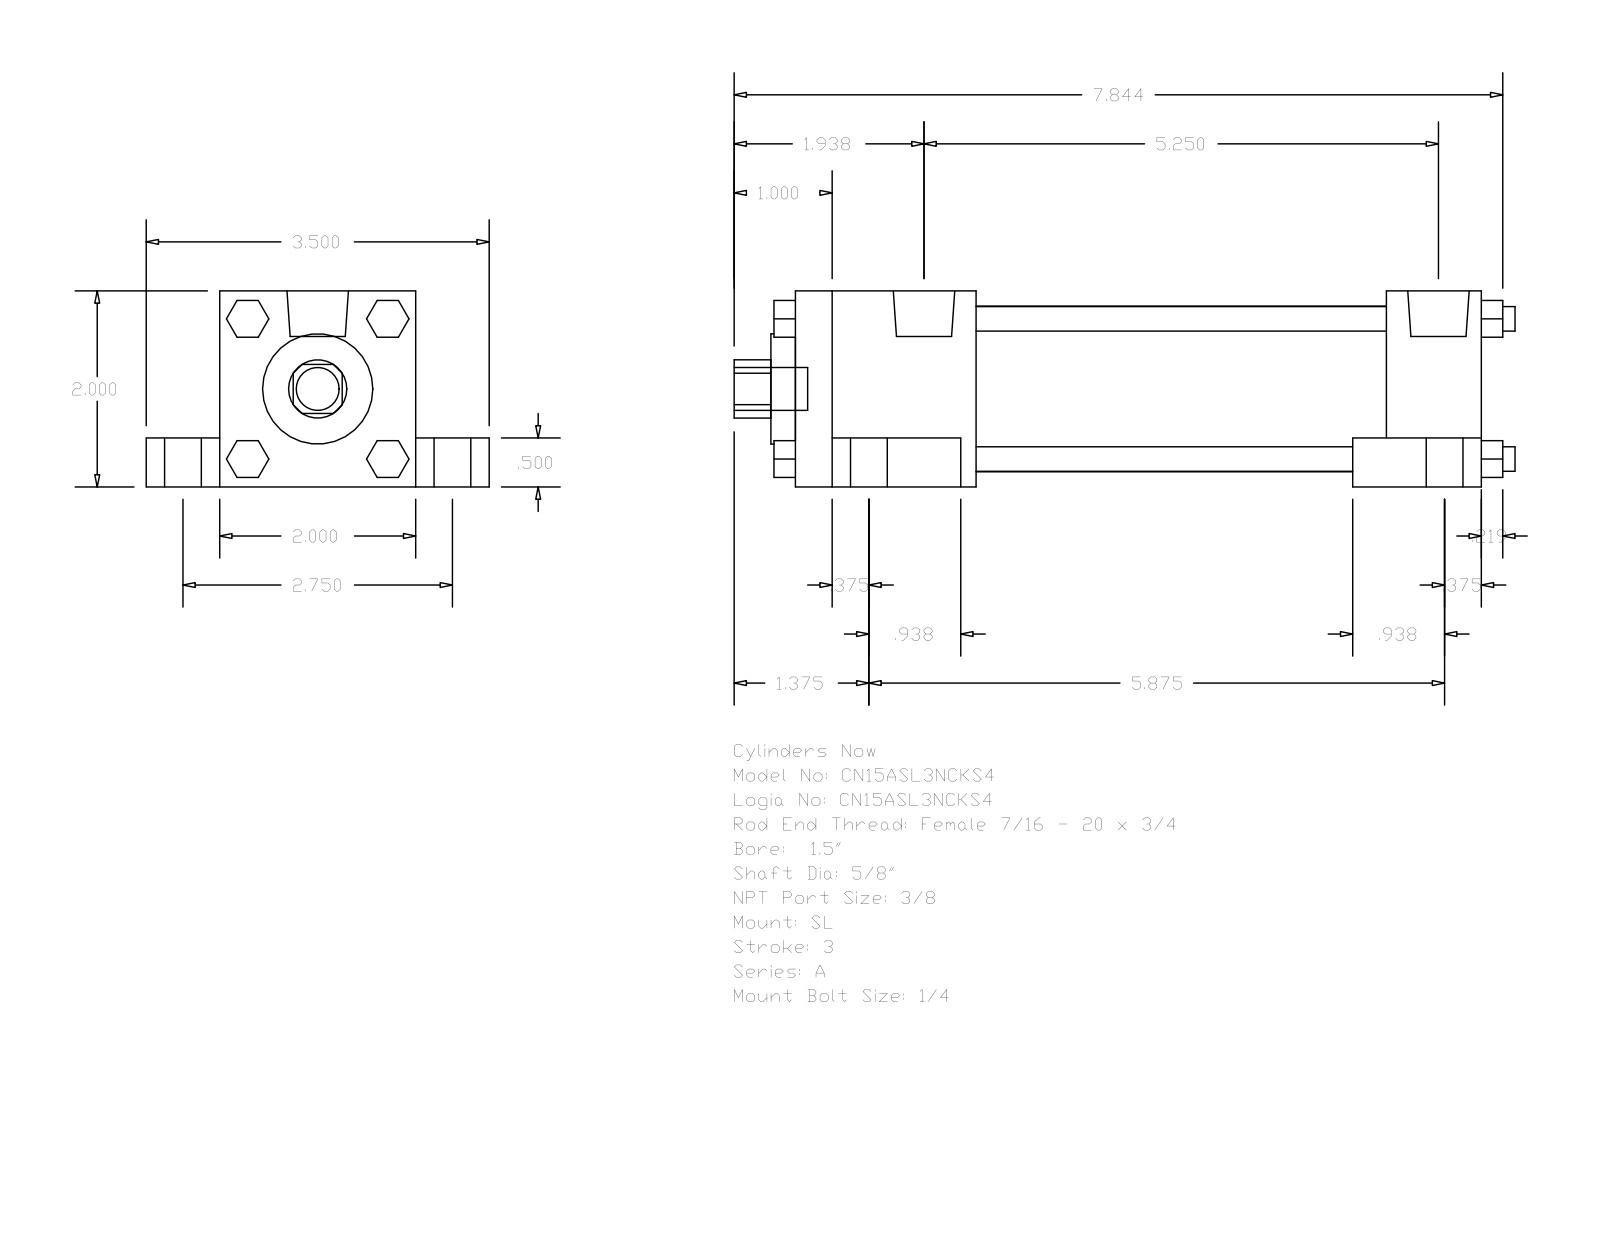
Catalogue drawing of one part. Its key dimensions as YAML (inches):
part_name: "A_SL__0150_0.625"
step_written_by: "GSSL Pune (CONFIG_CONTROL_DESIGN)"
units: inches
bodies: {solids: 0, faces: 148, planar: 112, cylindrical: 36, other: 0}
overall_size: [7.969, 3.5, 2]
round_holes:
  - {diameter: 0.625, count: 1}
  - {diameter: 1.125, count: 1}
  - {diameter: 1.69, count: 1}
round_bosses_or_shafts:
  - {diameter: 0.625, count: 4}
  - {diameter: 0.375, count: 4}
  - {diameter: 0.25, count: 4}
  - {diameter: 0.219, count: 4}
  - {diameter: 0.627, count: 2}
  - {diameter: 0.437, count: 1}
partial_cylinders:
  - {radius: 0.297, count: 1}
face_to_face_distances: [2, 0.75, 0.5, 1.5, 2.75, 7, 0.375, 1.313, 6.031, 0.969]
